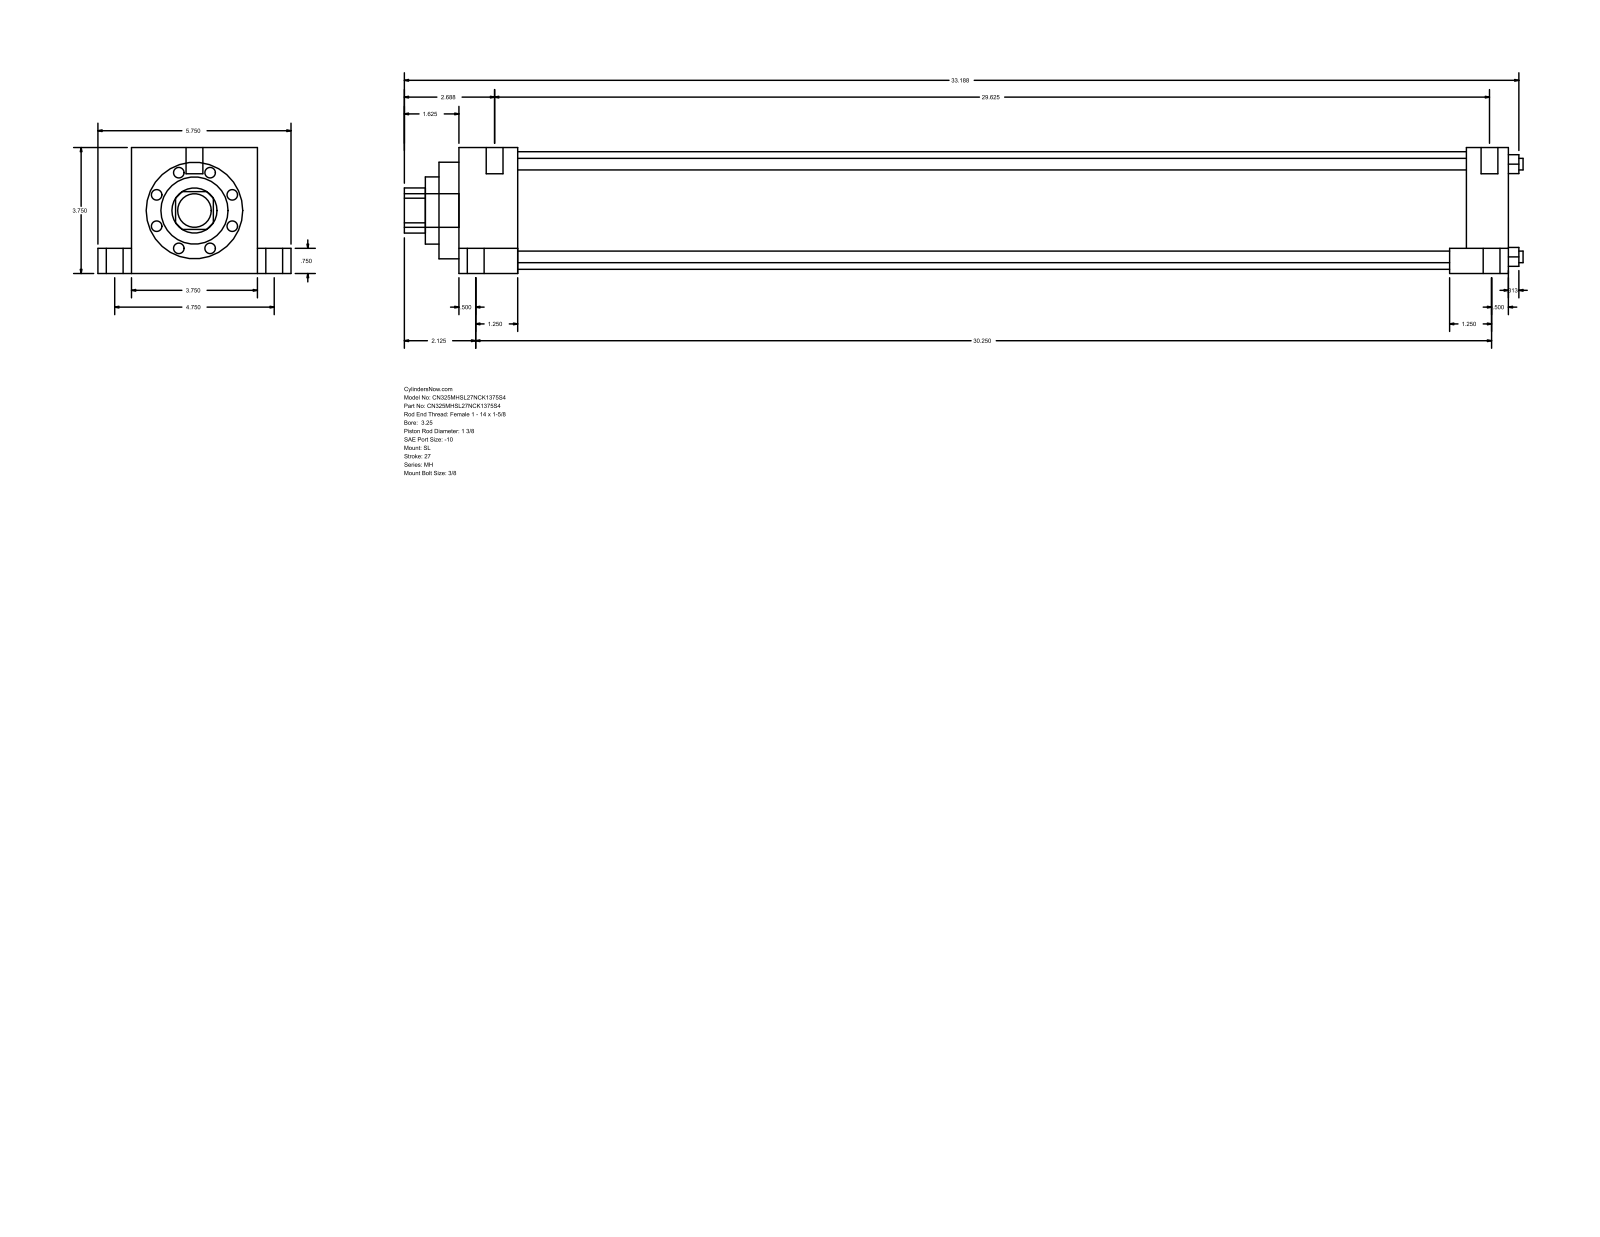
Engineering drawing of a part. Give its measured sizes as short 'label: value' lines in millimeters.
name: MH_SL__0325_1.375
written by: GSSL Pune (CONFIG_CONTROL_DESIGN)
unit: mm
bodies: 0 solids, 110 faces (77 planar, 33 cylindrical, 0 other)
size: 846.14 × 146.05 × 95.25
holes: 4× ⌀8.76, 1× ⌀34.92, 1× ⌀50.8, 1× ⌀73.03, 1× ⌀88.9
bosses: 6× ⌀12.7, 4× ⌀19.05, 4× ⌀5.56, 1× ⌀25.4
rounds: 1× R17.06
face distances: 95.24, 793.75, 44.45, 749.3, 25.41, 120.65, 19.05, 76.19, 762, 717.55
hole spacings: 49.57, 70.1, 99.14
